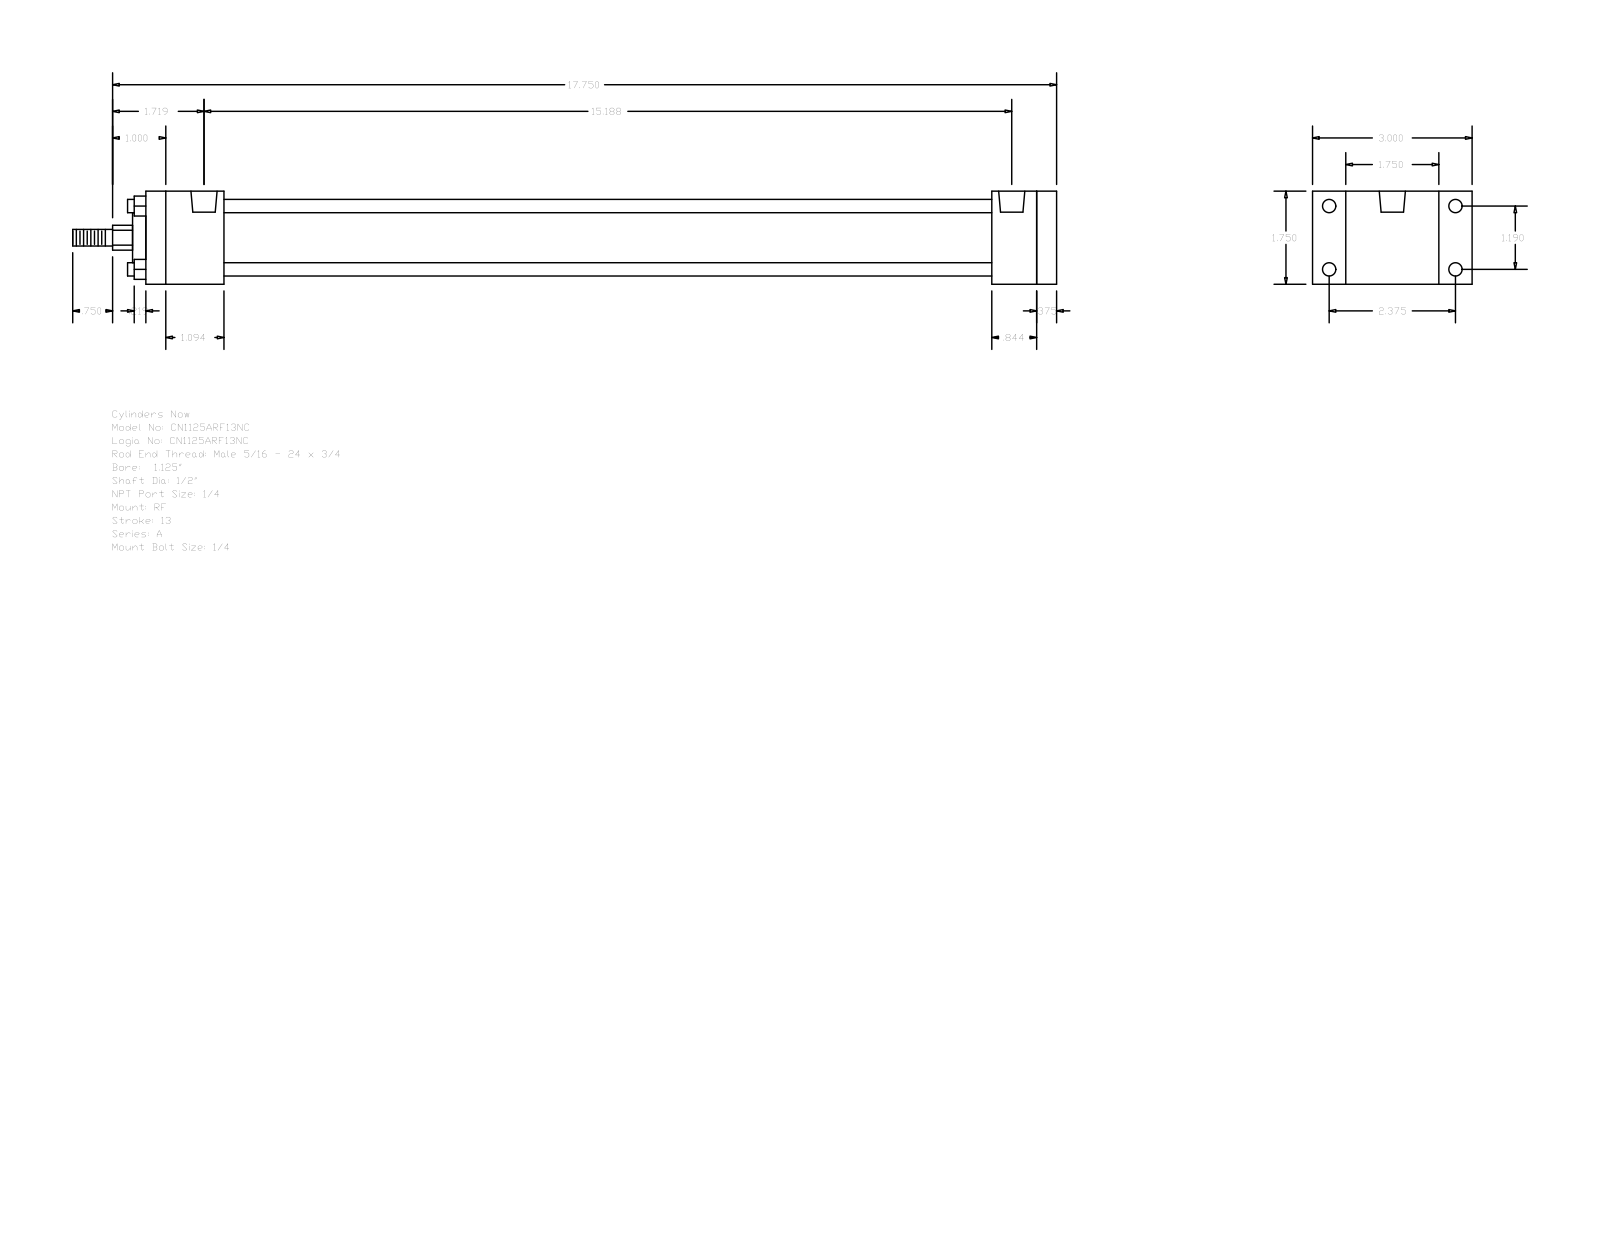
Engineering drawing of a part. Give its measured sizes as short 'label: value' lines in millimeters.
name: A_RF__0112_0.5
written by: GSSL Pune (CONFIG_CONTROL_DESIGN)
unit: mm
bodies: 0 solids, 92 faces (64 planar, 28 cylindrical, 0 other)
size: 469.9 × 76.2 × 44.45
holes: 4× ⌀5.56, 4× ⌀6.35, 2× ⌀12.49
bosses: 4× ⌀6.35, 1× ⌀31.88, 1× ⌀23.81, 1× ⌀12.7, 1× ⌀7.94
rounds: 1× R5.94
face distances: 44.46, 9.53, 434.97, 425.44, 37.3, 404.01, 366.71, 388.14, 397.67, 21.43
hole spacings: 30.22, 60.32, 67.47, 382.59, 1.58, 1.59, 384.17, 384.18
